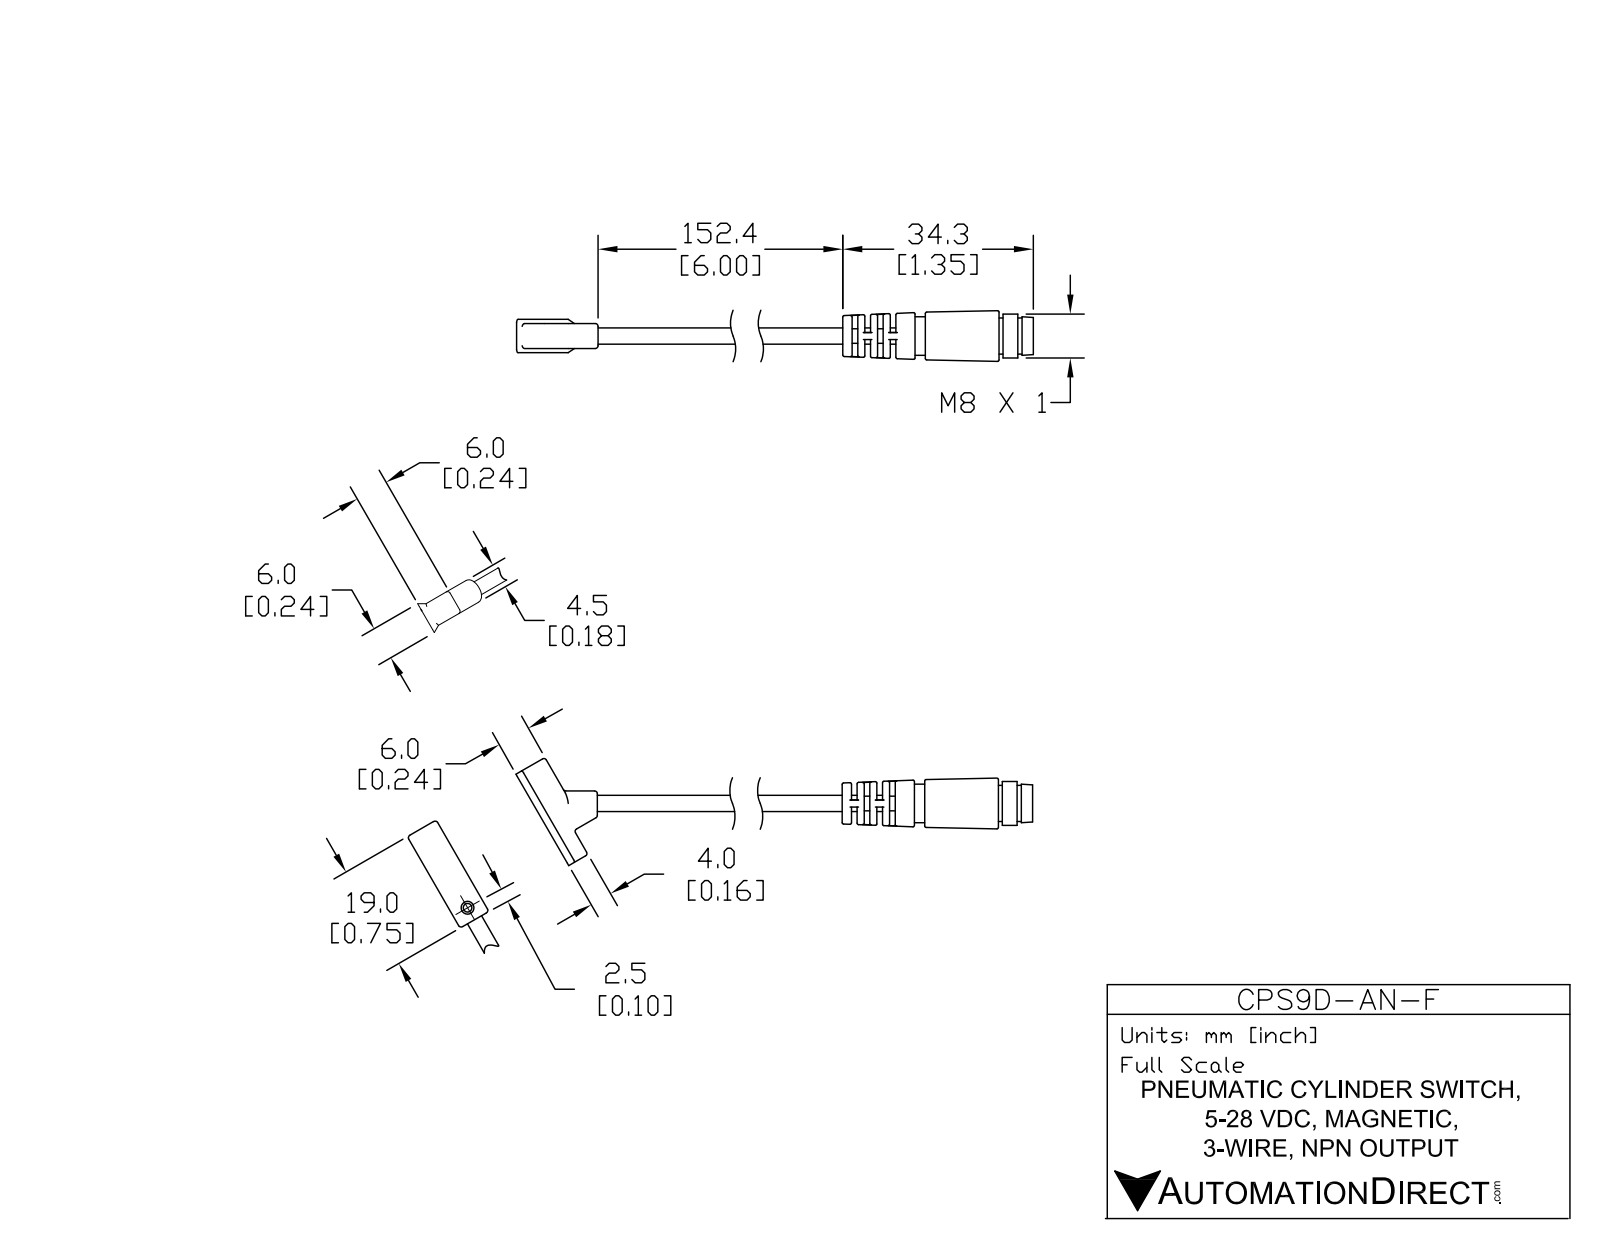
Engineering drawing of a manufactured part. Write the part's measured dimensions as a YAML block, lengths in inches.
part_name: "CPS9D-AN-F"
step_written_by: "SolidWorks 2014 (AUTOMOTIVE_DESIGN)"
units: inches
bodies: {solids: 1, faces: 168, planar: 58, cylindrical: 53, other: 57}
overall_size: [5.683, 3.597, 0.36]
volume: 0.178
surface_area: 4.666
round_holes:
  - {diameter: 0.091, count: 1}
  - {diameter: 0.227, count: 1}
round_bosses_or_shafts:
  - {diameter: 0.04, count: 3}
  - {diameter: 0.311, count: 1}
  - {diameter: 0.273, count: 1}
  - {diameter: 0.256, count: 1}
  - {diameter: 0.115, count: 1}
partial_cylinders:
  - {radius: 0.02, count: 20}
  - {radius: 0.089, count: 1}
face_to_face_distances: [0.09, 0.05, 0.04, 0.18, 0.177, 0.09, 0.13, 0.22, 0.27, 0.286]
